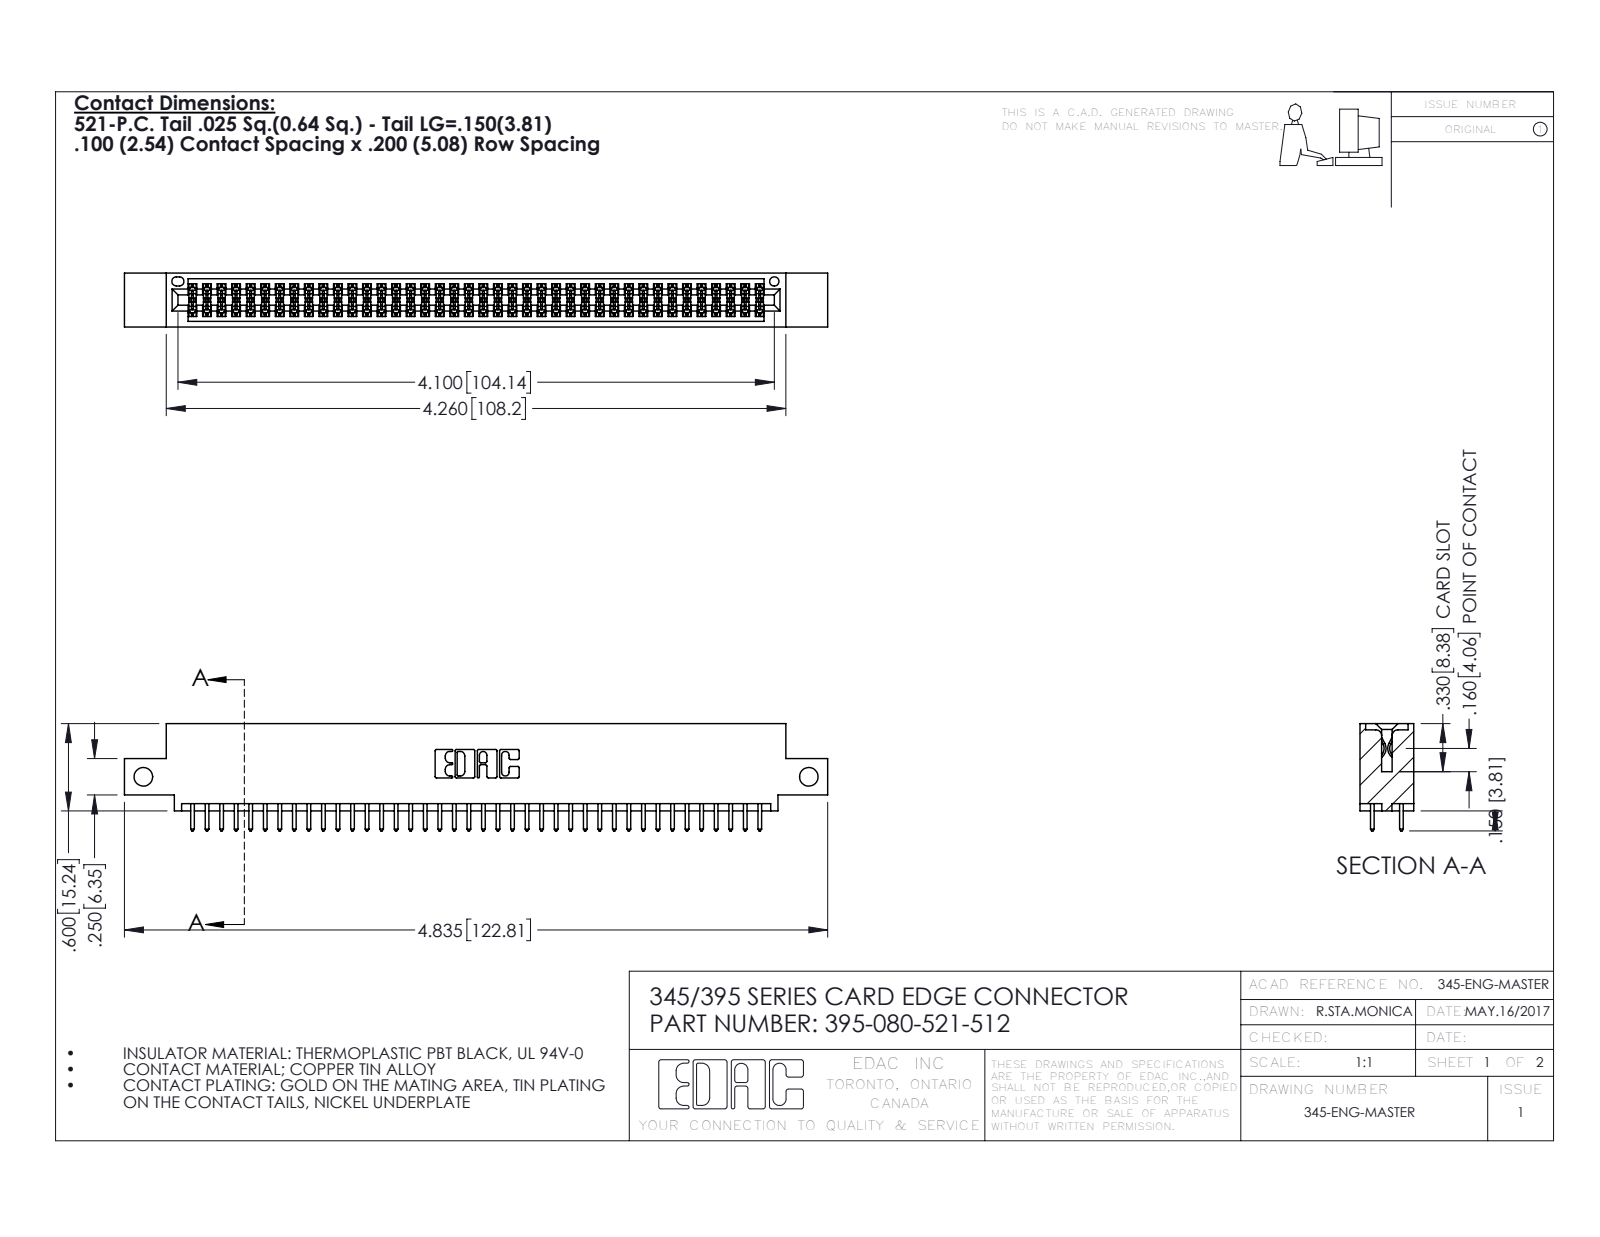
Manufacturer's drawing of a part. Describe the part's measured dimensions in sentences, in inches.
The part is named "345 Part_0.110 Offset - Side Mount; 395-080-521-512; 345-292-001_345-293-121". Its 3-D file was written by "SolidWorks 2016 (CONFIG_CONTROL_DESIGN)". It is 81 solids with 4130 faces: 2724 planar, 1406 cylindrical and 0 other. Overall it measures 4.835 by 0.737 by 0.37 inches. Its volume is 0.715 cubic inches and its surface area 26.39 square inches. Round holes: 2 of diameter 0.128, 1 of diameter 0.064. Partial cylindrical surfaces (rounded edges, fillets, slot ends): 120 of radius 0.006, 80 of radius 0.01, 22 of radius 0.01, 6 of radius 0.007, 6 of radius 0.031, 3 of radius 0.026, 2 of radius 0.014, 2 of radius 0.019. The main face-to-face distances are 0.298, 0.072, 0.2, 0.37, 0.098, 0.272, 0.025, 0.225, 0.175, 0.149. The hole center spacings are 4.575.
